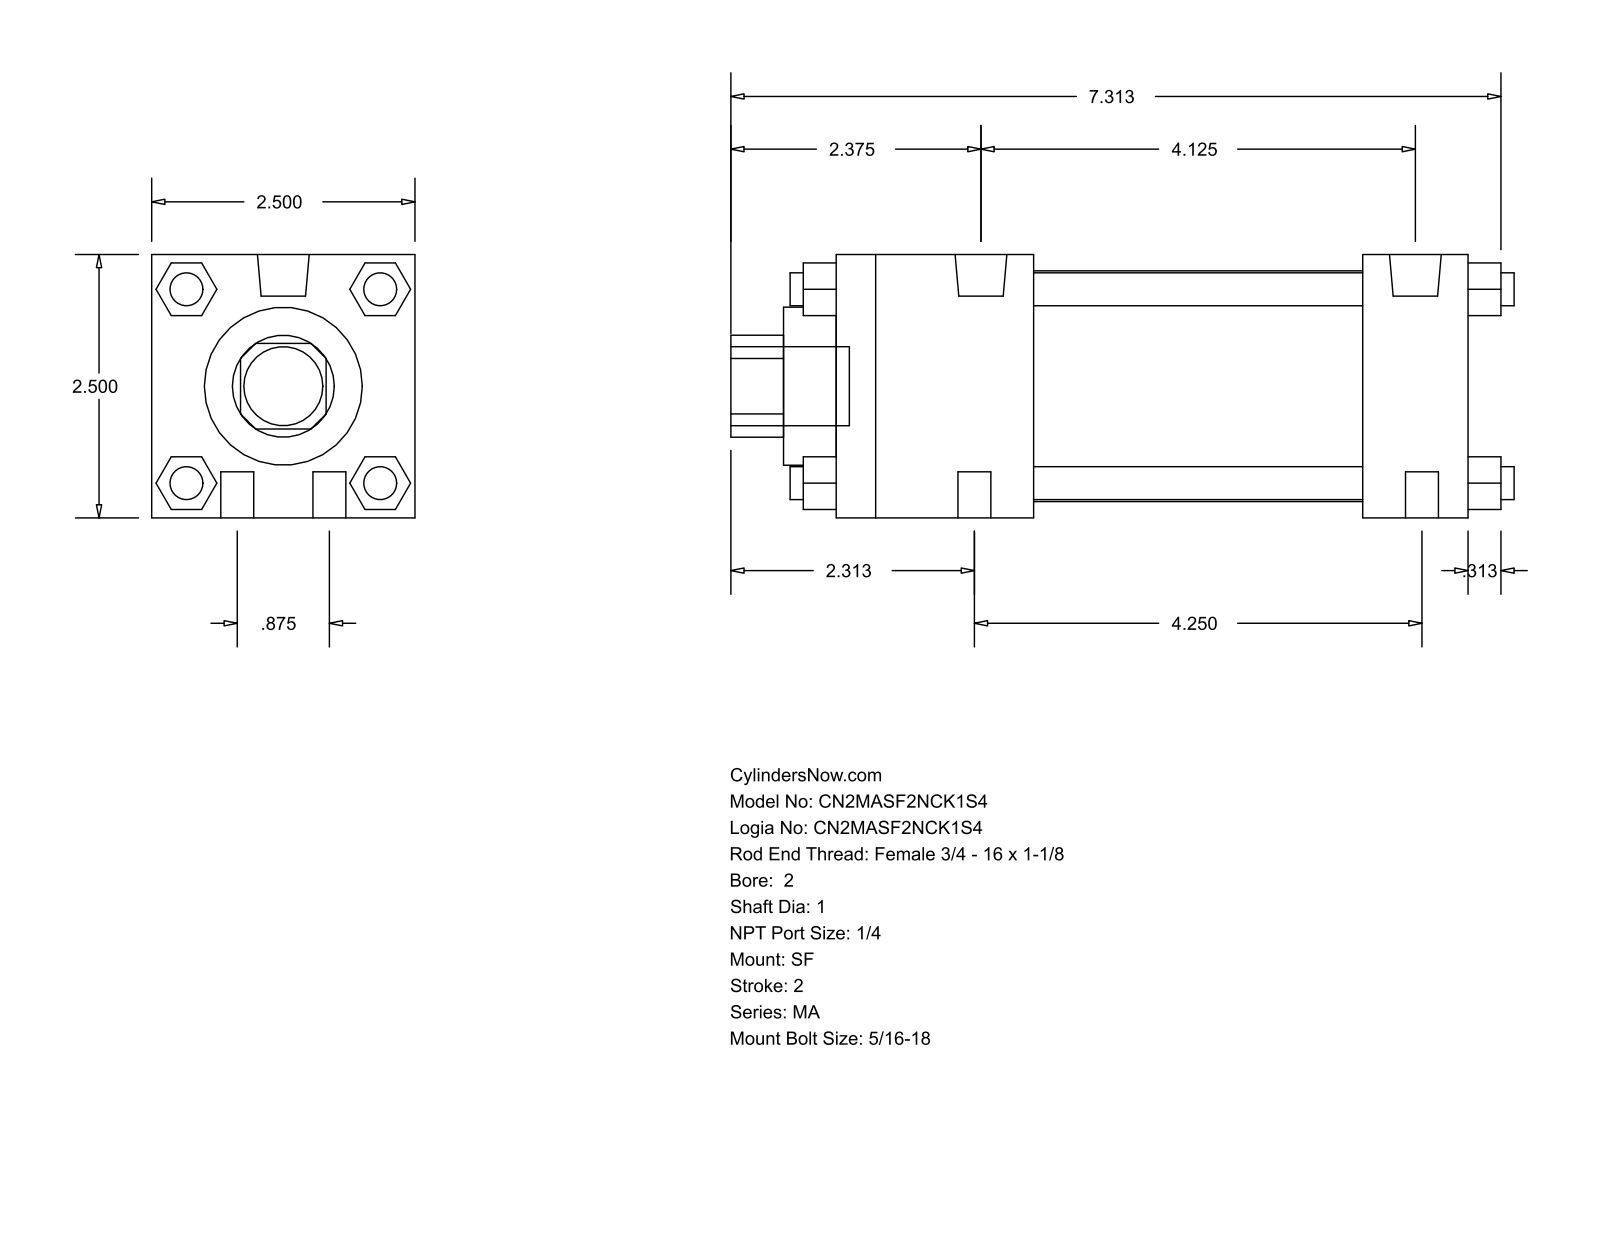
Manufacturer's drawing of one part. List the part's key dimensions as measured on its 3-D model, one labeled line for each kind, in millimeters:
Part name (STEP PRODUCT): MA_SF__0200_1
STEP written by: GSSL Pune (CONFIG_CONTROL_DESIGN)
Units: millimetres
Bodies: 0 solids, 124 faces (94 planar, 30 cylindrical, 0 other)
Overall size (bounding box): 188.91 × 63.5 × 63.5
Round holes (diameter × count): ⌀25.4 ×1, ⌀38.1 ×1, ⌀55.63 ×1
Round bosses / shafts (diameter × count): ⌀7.94 ×10, ⌀12.49 ×2, ⌀19.05 ×1
Partial cylindrical surfaces — rounded edges, fillets, slot ends (radius × count): R12.29 ×1
Main face-to-face distances: 63.5, 152.4, 12.7, 25.4, 127, 47.63, 79.37, 104.77, 23.37, 40.47
